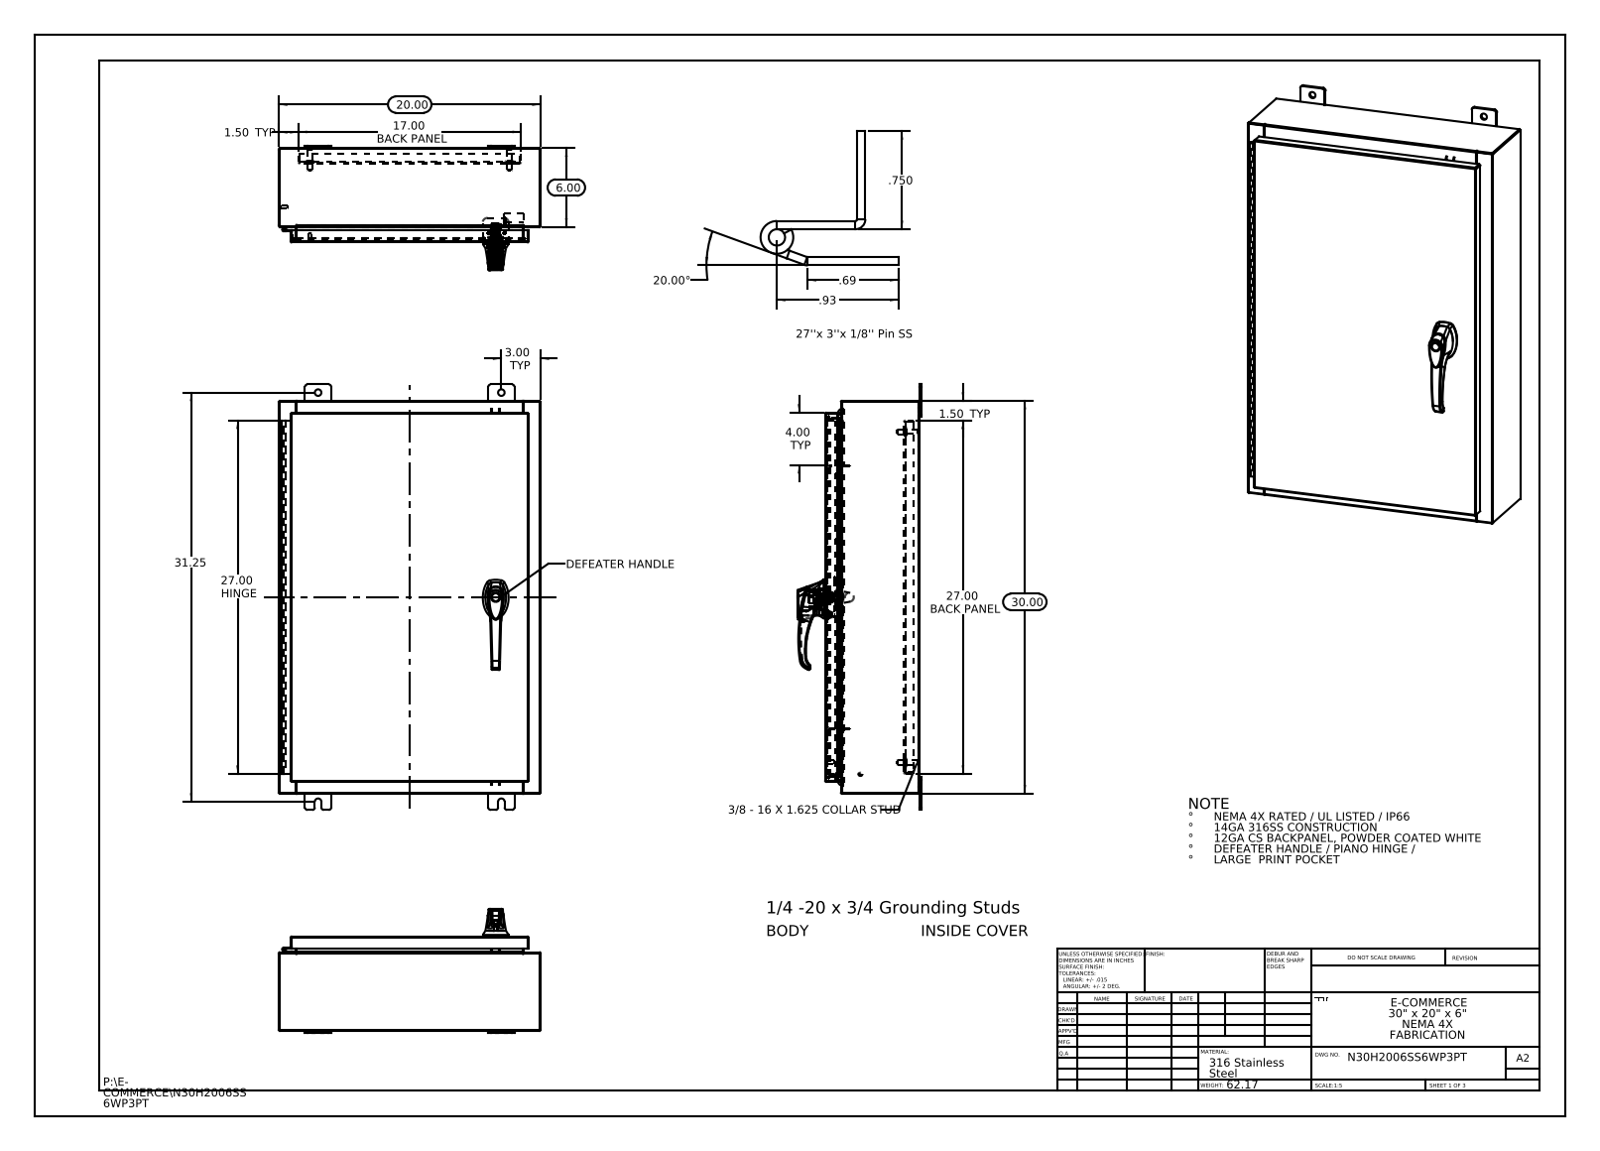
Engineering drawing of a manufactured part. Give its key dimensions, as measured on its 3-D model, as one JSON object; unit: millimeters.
{"part_name": "N30H2006SS6WP3PT Body; 00005309_G26103101; 10_30 CD Stud; 2616310101 (+8 more)", "step_written_by": "SolidWorks 2013 (CONFIG_CONTROL_DESIGN)", "units": "millimeters", "bodies": {"solids": 37, "faces": 2662, "planar": 971, "cylindrical": 993, "other": 698}, "overall_size": [825.5, 508, 241.2], "volume_mm3": 3631000, "surface_area_mm2": 3513000, "round_holes": [[12.7, 8], [6.4, 4], [3.5, 3], [4.1, 3], [2, 2], [5.2, 2], [8, 2], [11.1, 2], [3.2, 1], [3.2, 1], [5, 1], [7, 1]], "round_bosses_or_shafts": [[15.9, 4], [9.5, 4], [8.4, 4], [4, 4], [3.6, 4], [8, 3], [6, 3], [30, 1]], "partial_cylinders_radius": [[3, 37], [0.2, 33], [0.3, 24], [4.8, 24], [2.2, 18], [1, 15], [0.7, 12], [0.2, 6]], "face_to_face_distances": [1.9, 181, 2.6, 179.1, 182.9, 25.4, 27.3, 153.7, 155.6, 29.9], "hole_center_spacings": [212.6, 384.6, 7.5, 15.9, 21.4, 31.8, 33.4, 39.6]}
